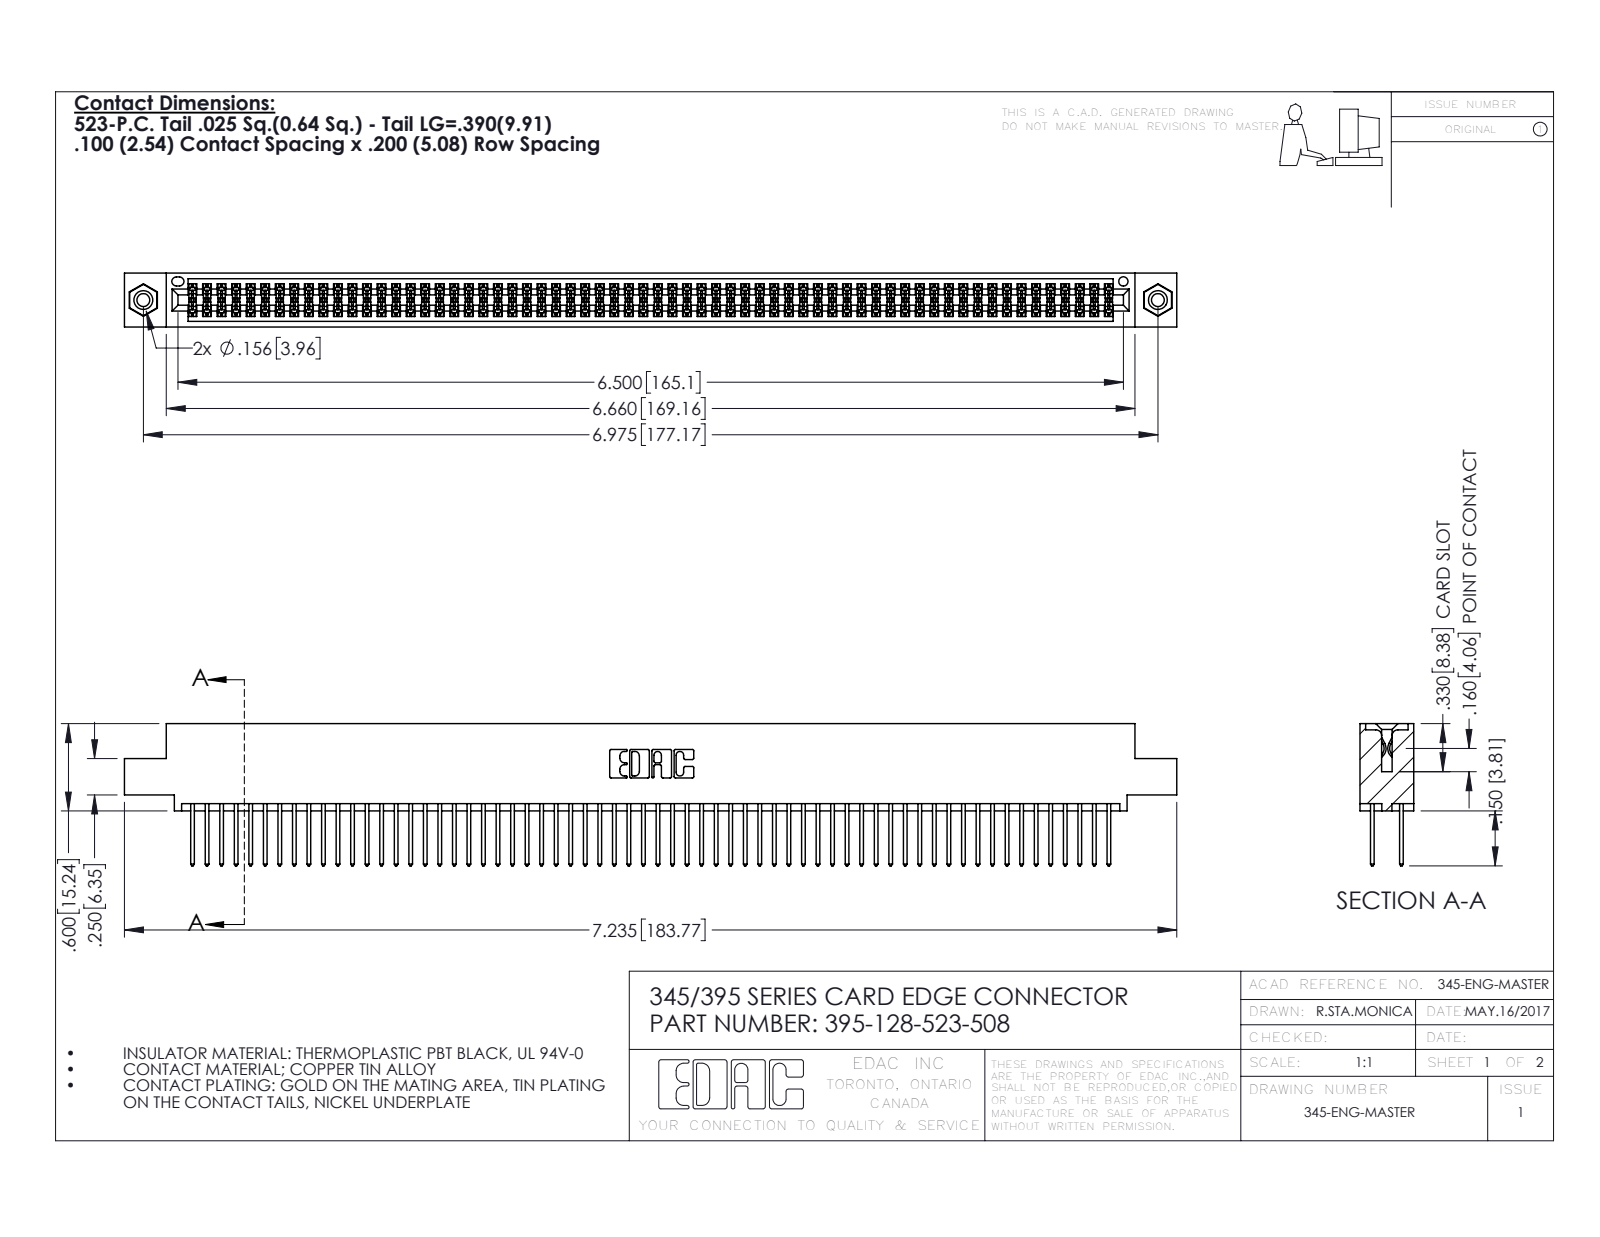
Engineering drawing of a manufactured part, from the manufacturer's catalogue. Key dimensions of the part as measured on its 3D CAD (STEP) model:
Part name (STEP PRODUCT): 345 Part_0.110 Offset - 0.156 Dia-TI; 345-250-001_345-250-003-102; 345-292-001_345-293-123; 395-128-523-508
STEP written by: SolidWorks 2016 (CONFIG_CONTROL_DESIGN)
Units: inches
Bodies: 131 solids, 6590 faces (4340 planar, 2234 cylindrical, 16 other)
Overall size (bounding box): 7.235 × 0.977 × 0.37
Volume: 1.113 in³ · Surface area: 44.44 in²
Round holes (diameter × count): ⌀0.089 ×2, ⌀0.125 ×2, ⌀0.156 ×2, ⌀0.064 ×1
Round bosses / shafts (diameter × count): ⌀0.155 ×2
Partial cylindrical surfaces — rounded edges, fillets, slot ends (radius × count): R0.006 ×192, R0.01 ×128, R0.01 ×22, R0.007 ×6, R0.031 ×6, R0.026 ×3, R0.014 ×2, R0.019 ×2
Main face-to-face distances: 0.072, 0.298, 0.2, 0.098, 0.272, 0.025, 0.37, 0.225, 0.175, 0.149
Hole centre spacings: 0.27, 6.739, 6.975
